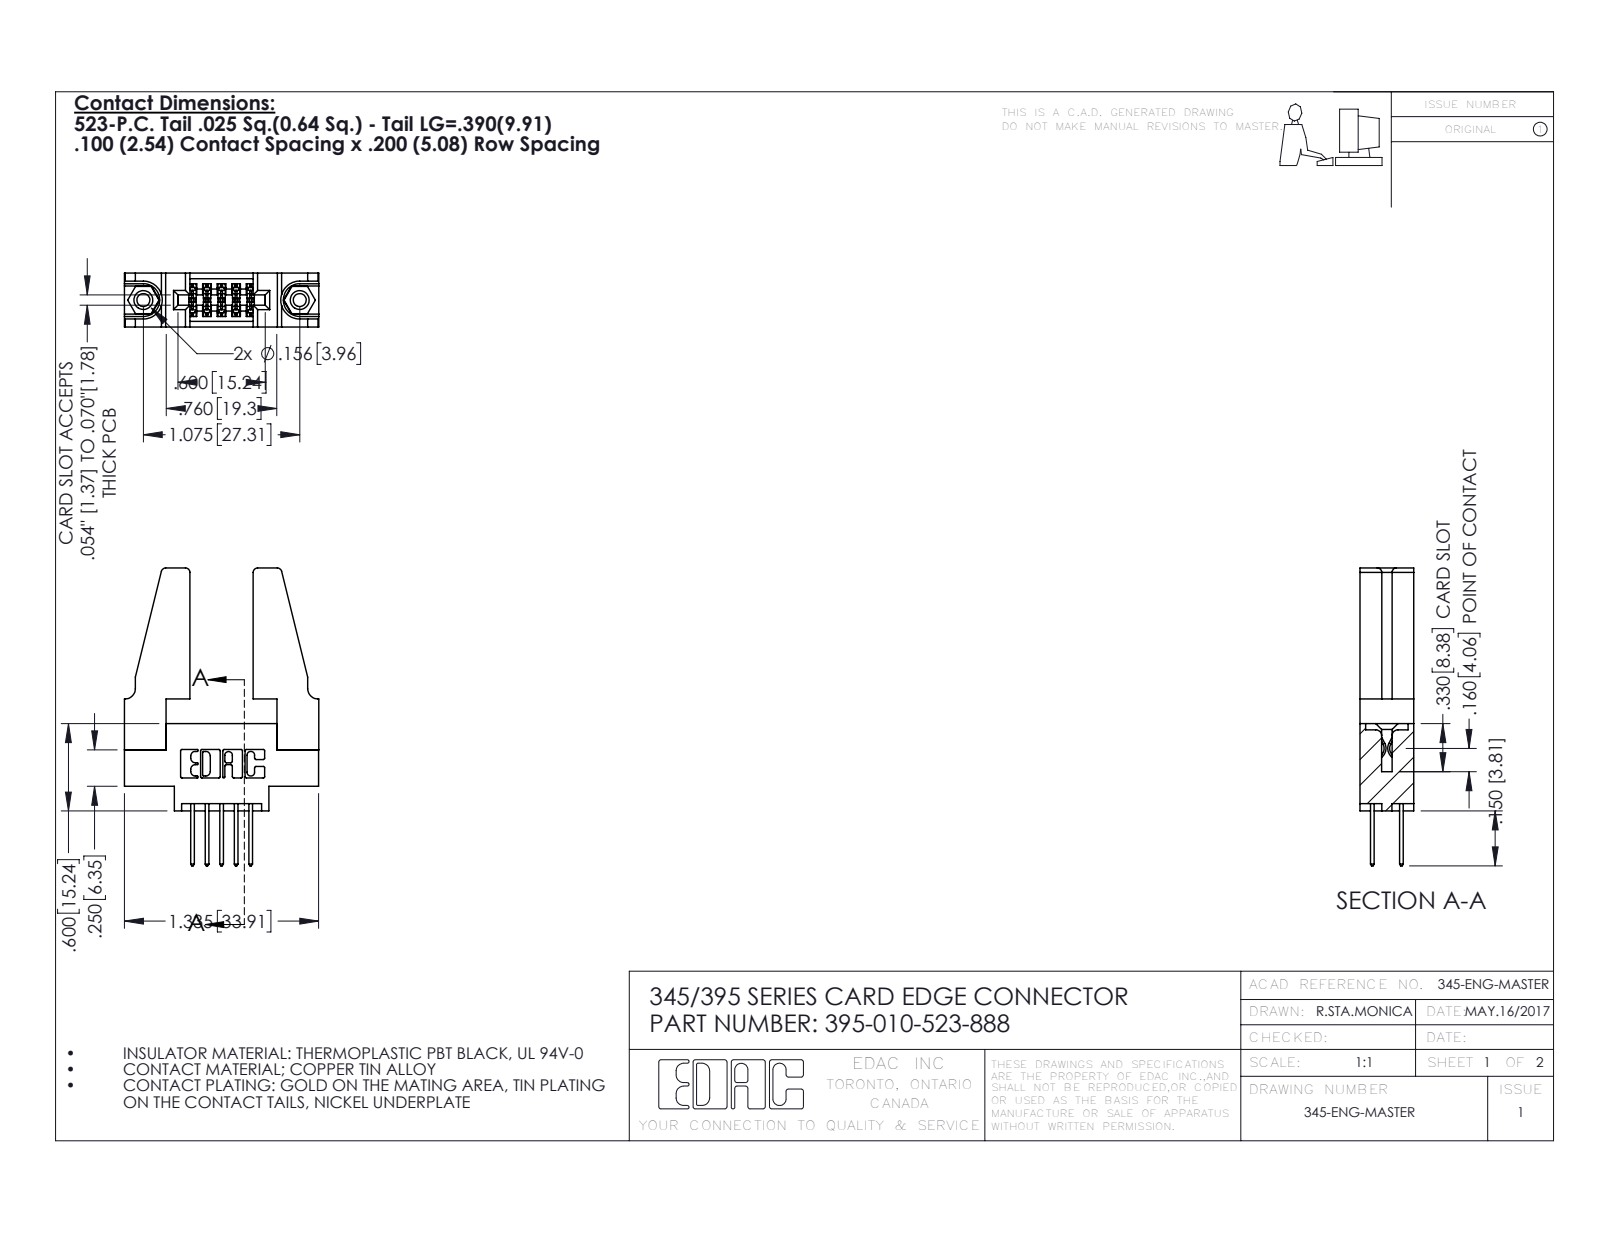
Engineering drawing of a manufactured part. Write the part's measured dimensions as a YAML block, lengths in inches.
part_name: "345 Part_0.170 Offset - 0.156 Dia-TH; 345-250-001_345-250-001-102; 395-010-523-888; 345-220-078_345-220-088 (+1 more)"
step_written_by: "SolidWorks 2016 (CONFIG_CONTROL_DESIGN)"
units: inches
bodies: {solids: 15, faces: 754, planar: 486, cylindrical: 252, other: 16}
overall_size: [2.047, 1.336, 0.37]
volume: 0.373
surface_area: 10.65
round_holes:
  - {diameter: 0.089, count: 2}
  - {diameter: 0.125, count: 2}
  - {diameter: 0.156, count: 2}
  - {diameter: 0.064, count: 1}
round_bosses_or_shafts:
  - {diameter: 0.155, count: 2}
partial_cylinders:
  - {radius: 0.01, count: 22}
  - {radius: 0.006, count: 15}
  - {radius: 0.01, count: 10}
  - {radius: 0.03, count: 8}
  - {radius: 0.007, count: 6}
  - {radius: 0.031, count: 6}
  - {radius: 0.026, count: 3}
  - {radius: 0.014, count: 2}
face_to_face_distances: [0.37, 0.072, 0.298, 0.2, 0.098, 0.272, 0.025, 0.148, 0.15, 0.225]
hole_center_spacings: [0.27, 0.847, 1.075]
